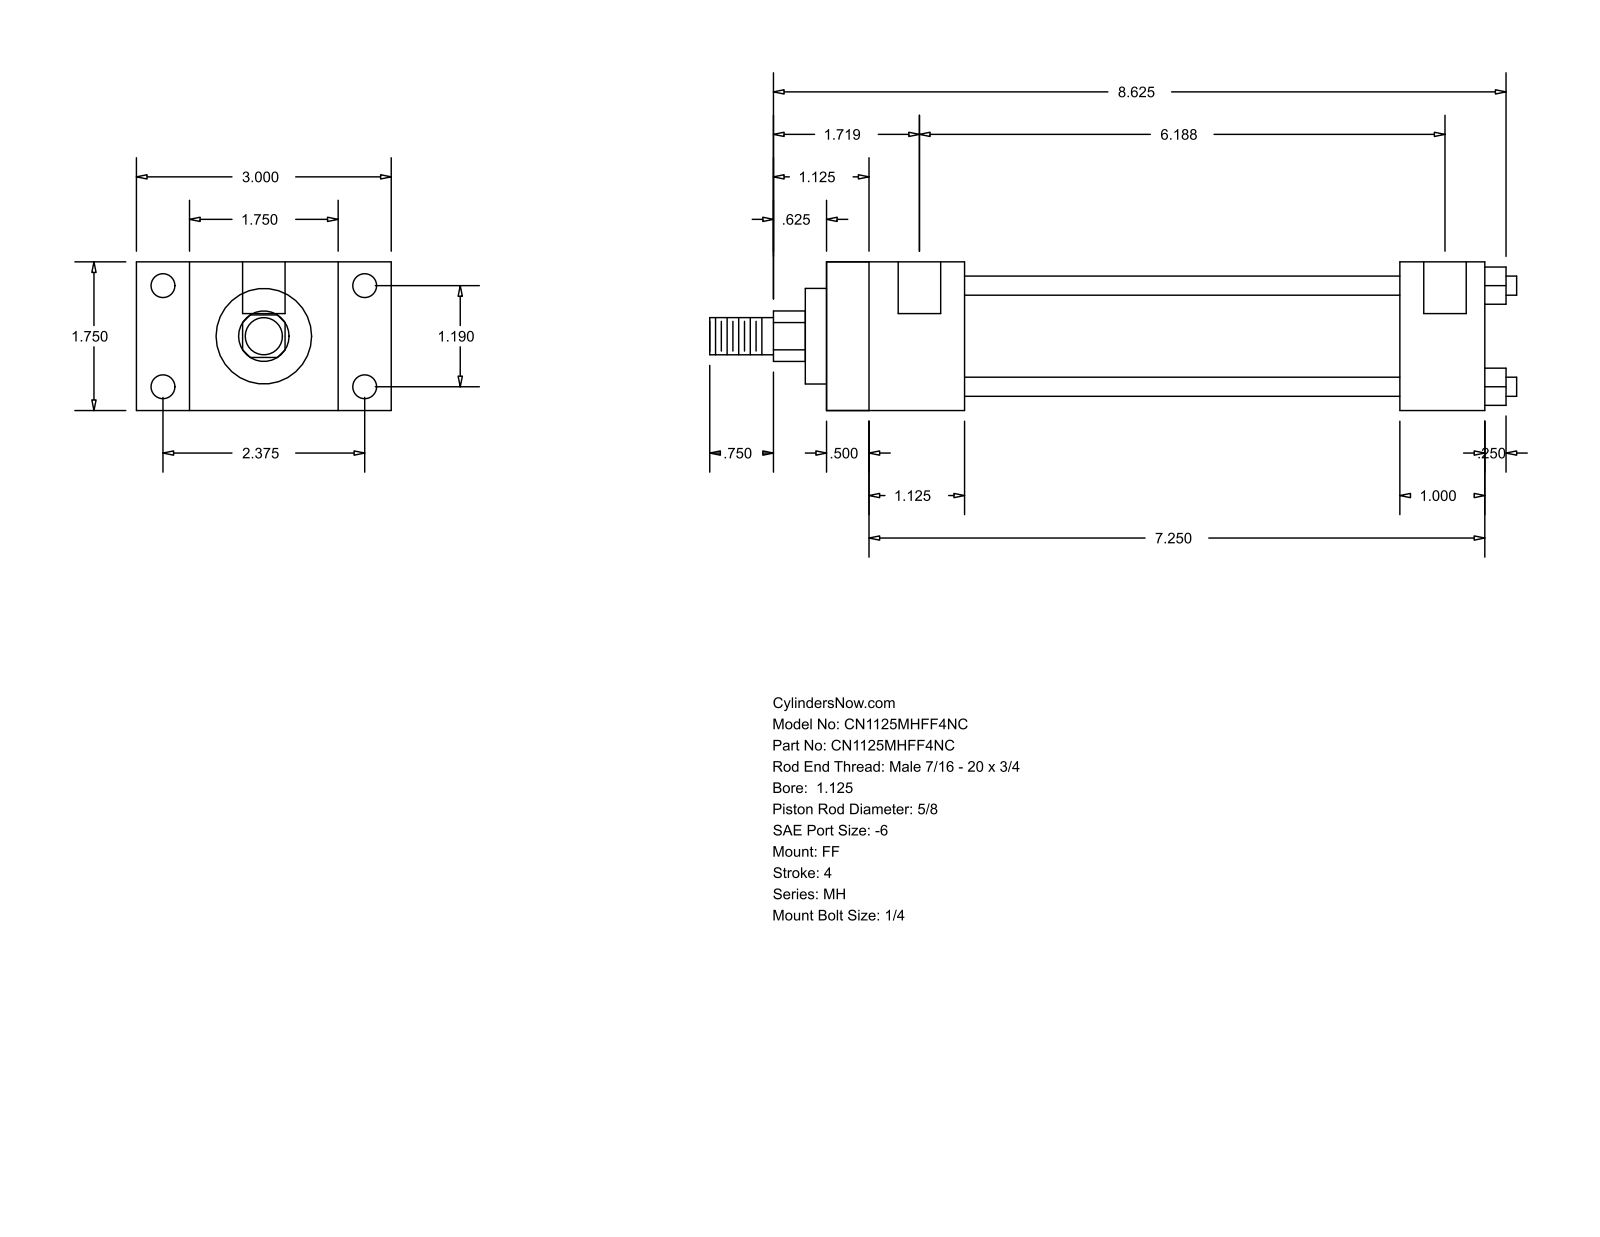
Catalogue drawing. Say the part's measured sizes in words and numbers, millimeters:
The part is named "MH_FF__0112_0.625". Its 3-D file was written by "GSSL Pune (CONFIG_CONTROL_DESIGN)". It is 0 solids with 92 faces: 64 planar, 28 cylindrical and 0 other. Overall it measures 241.3 by 76.2 by 44.45 millimeters. Round holes: 4 of diameter 5.56, 4 of diameter 7.14, 2 of diameter 12.7. Round bosses or shafts: 4 of diameter 5.71, 1 of diameter 34.92, 1 of diameter 28.57, 1 of diameter 15.88, 1 of diameter 11.11. Partial cylindrical surfaces (rounded edges, fillets, slot ends): 1 of radius 7.54. The main face-to-face distances are 44.46, 196.84, 15.87, 12.69, 184.15, 28.58, 60.33, 25.4, 41.27, 171.44. The hole center spacings are 30.22, 60.32, 67.47, 153.99, 3.17, 157.16.
